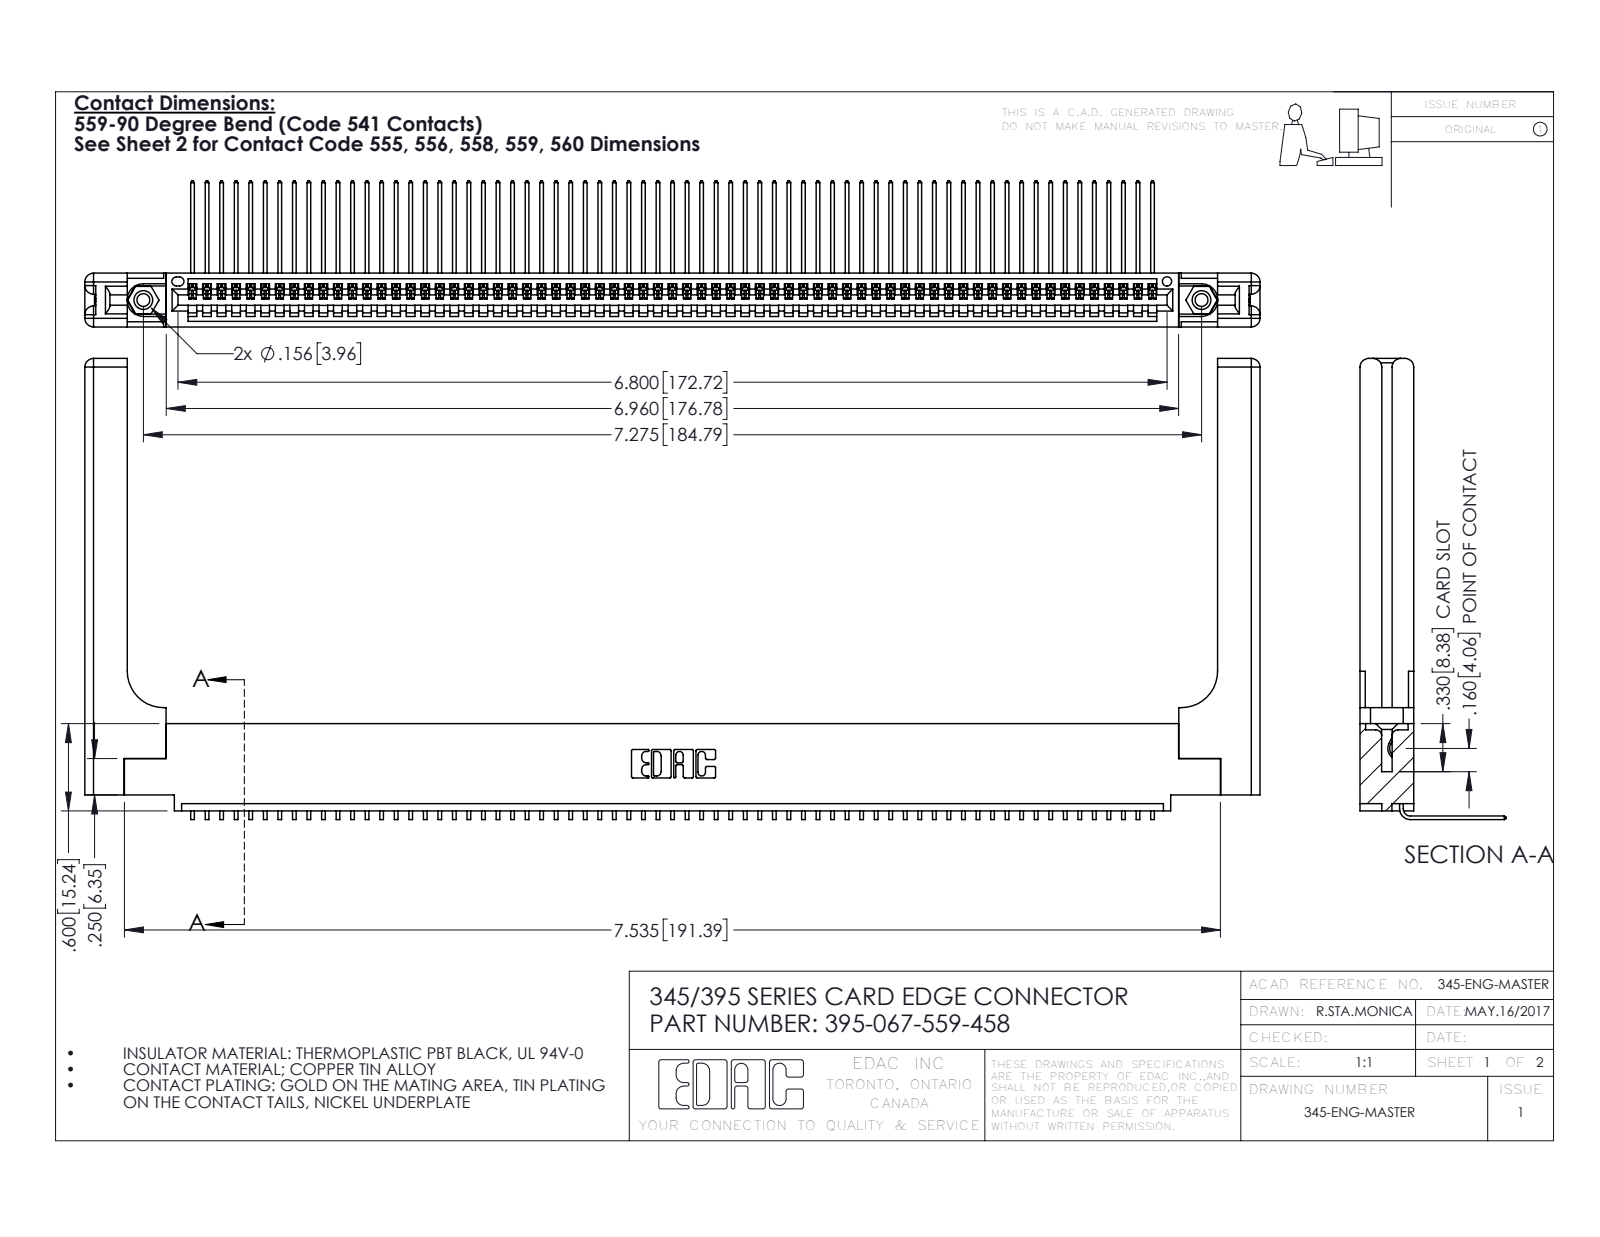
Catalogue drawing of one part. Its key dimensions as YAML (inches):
part_name: "395-067-559-458; 345-250-001_345-250-001-102; 345 Part_0.110 Offset - 0.156 Dia-TH; 345-220-058_345-220-058 (+1 more)"
step_written_by: "SolidWorks 2016 (CONFIG_CONTROL_DESIGN)"
units: inches
bodies: {solids: 72, faces: 4406, planar: 3046, cylindrical: 1300, other: 60}
overall_size: [8.079, 3.169, 1.005]
volume: 1.73
surface_area: 51.79
round_holes:
  - {diameter: 0.089, count: 2}
  - {diameter: 0.125, count: 2}
  - {diameter: 0.156, count: 2}
  - {diameter: 0.064, count: 1}
round_bosses_or_shafts:
  - {diameter: 0.155, count: 2}
partial_cylinders:
  - {radius: 0.006, count: 134}
  - {radius: 0.01, count: 22}
  - {radius: 0.06, count: 16}
  - {radius: 0.007, count: 6}
  - {radius: 0.031, count: 6}
  - {radius: 0.026, count: 3}
  - {radius: 0.03, count: 2}
  - {radius: 0.031, count: 2}
face_to_face_distances: [0.072, 0.37, 0.298, 0.098, 0.272, 0.025, 0.2, 0.225, 0.148, 0.15]
hole_center_spacings: [0.27, 7.039, 7.275]
